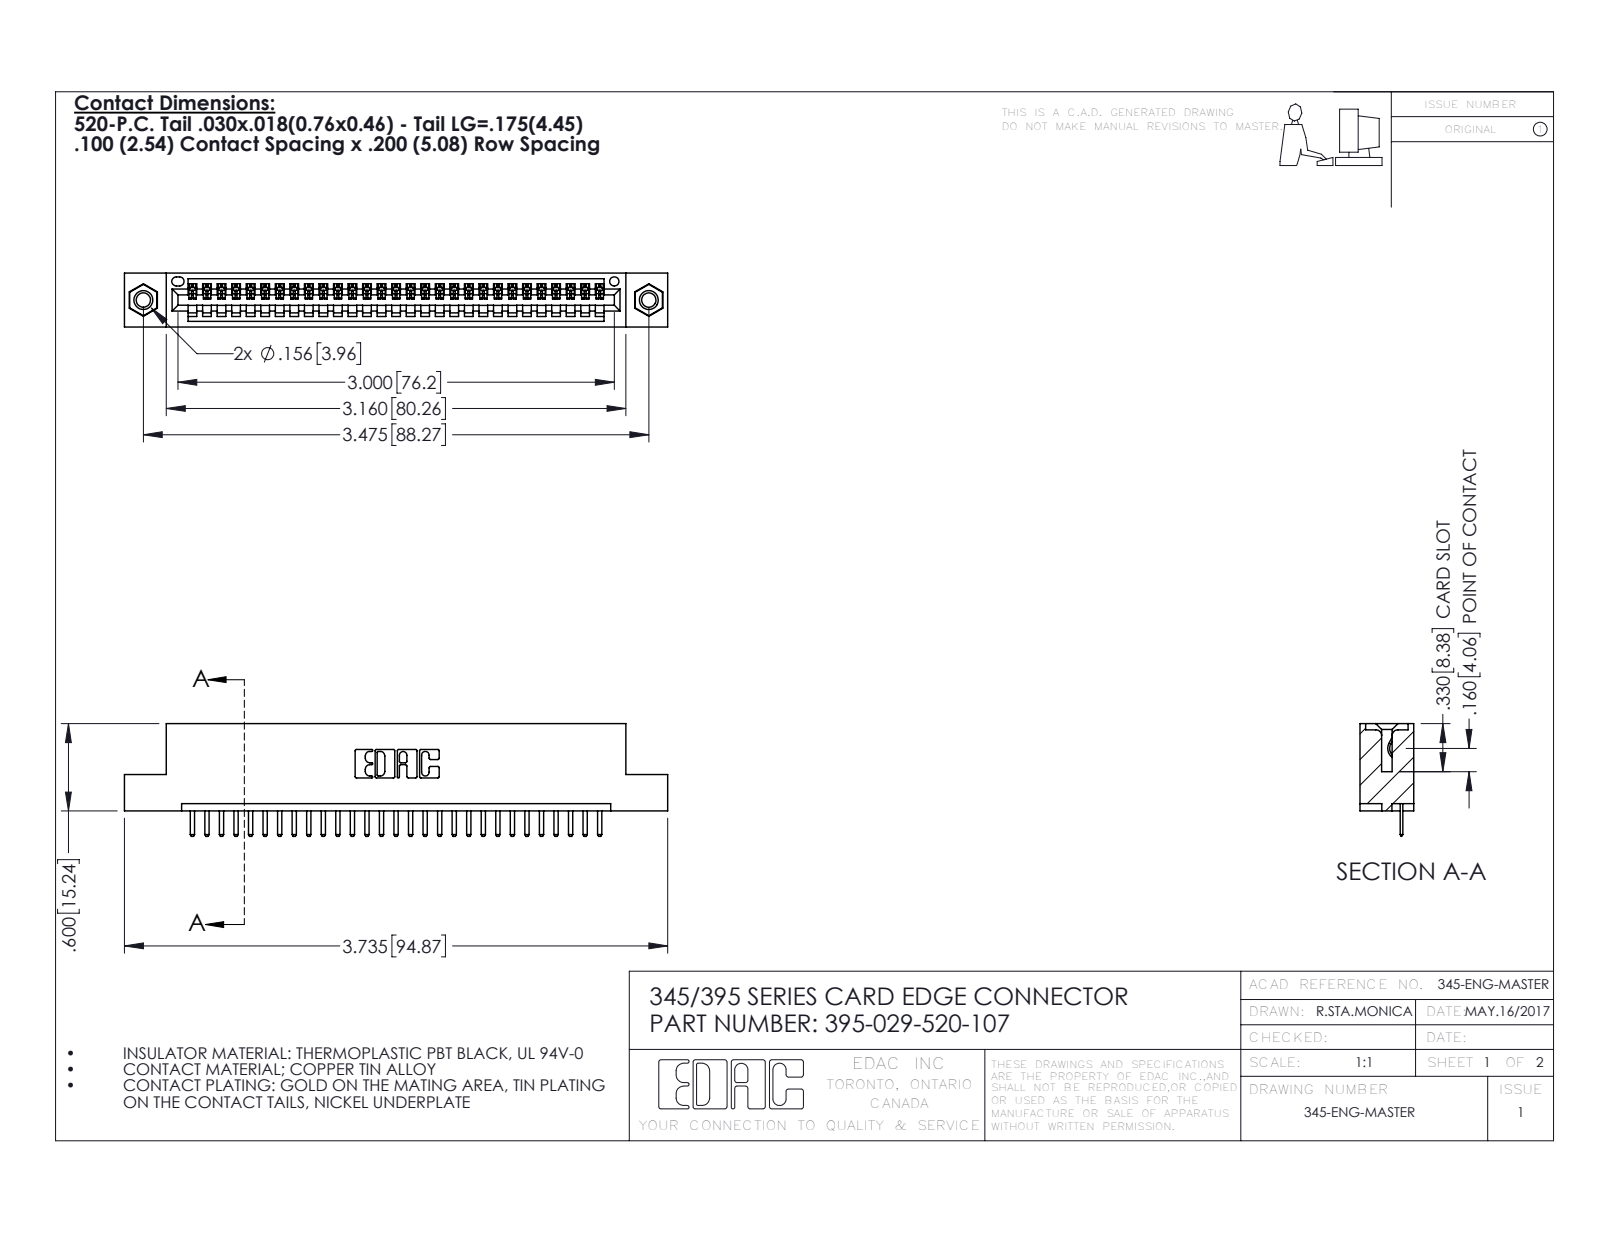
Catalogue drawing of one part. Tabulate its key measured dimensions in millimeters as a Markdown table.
| quantity | value |
| --- | --- |
| part name | 345-292-001_345-293-120; 345 Part_Flush Mounting Lugs - 0.156 Dia-TI; 345-250-001_345-250-005-103; 395-029-520-107 |
| STEP written by | SolidWorks 2016 (CONFIG_CONTROL_DESIGN) |
| units | millimeters |
| bodies | 32 solids, 1984 faces (1330 planar, 638 cylindrical, 16 other) |
| overall size | 94.9 × 19.7 × 9.4 |
| volume | 8 800 mm³ |
| surface area | 11 290 mm² |
| round holes (diameter × count) | 2.5 × 2, 3.2 × 2, 4 × 2, 1.6 × 1 |
| round bosses / shafts (diameter × count) | 3.9 × 2 |
| partial cylindrical surfaces (radius × count) | 0.3 × 60, 0.2 × 58, 0.3 × 22, 0.2 × 6, 0.8 × 6, 0.7 × 3, 0.8 × 2, 1 × 2 |
| main face-to-face distances | 1.8, 7.6, 9.4, 5.1, 2.5, 6.9, 0.6, 5.7, 1.8, 3.8 |
| hole center spacings | 6.9, 82.3, 88.3 |
